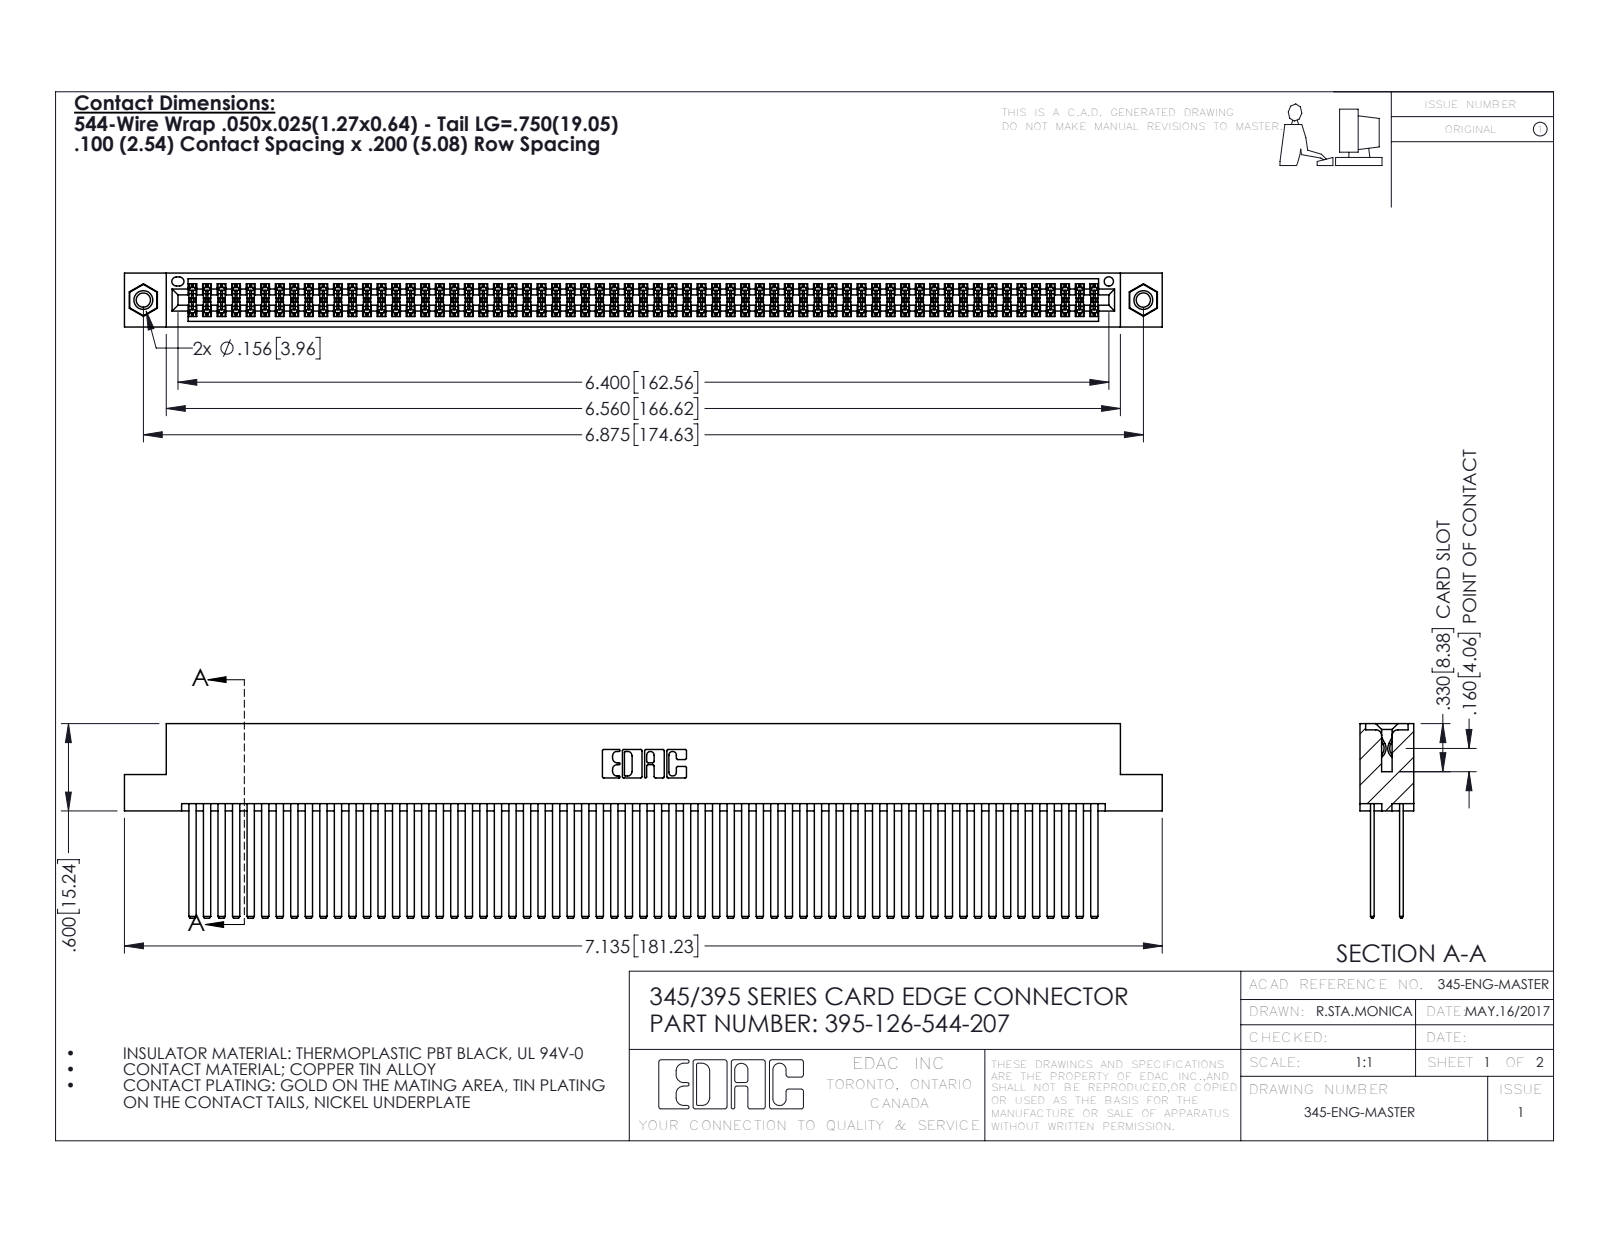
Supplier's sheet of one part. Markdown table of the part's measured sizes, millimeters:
| quantity | value |
| --- | --- |
| part name | 345 Part_Flush Mounting Lugs - 0.156 Dia-TI; 345-250-001_345-250-005-103; 345-292-001_345-293-144; 395-126-544-207 |
| STEP written by | SolidWorks 2016 (CONFIG_CONTROL_DESIGN) |
| units | millimeters |
| bodies | 129 solids, 5730 faces (3766 planar, 1948 cylindrical, 16 other) |
| overall size | 181.2 × 34 × 9.4 |
| volume | 19 550 mm³ |
| surface area | 34 520 mm² |
| round holes (diameter × count) | 2.5 × 2, 3.2 × 2, 4 × 2, 1.6 × 1 |
| round bosses / shafts (diameter × count) | 3.9 × 2 |
| partial cylindrical surfaces (radius × count) | 0.2 × 189, 0.3 × 22, 0.2 × 6, 0.8 × 6, 0.7 × 3, 0.4 × 2, 0.5 × 2, 0.6 × 2 |
| main face-to-face distances | 5.1, 0.6, 1.8, 2.5, 6.9, 7.6, 5.7, 4.4, 9.4, 1.3 |
| hole center spacings | 6.9, 168.6, 174.6 |
